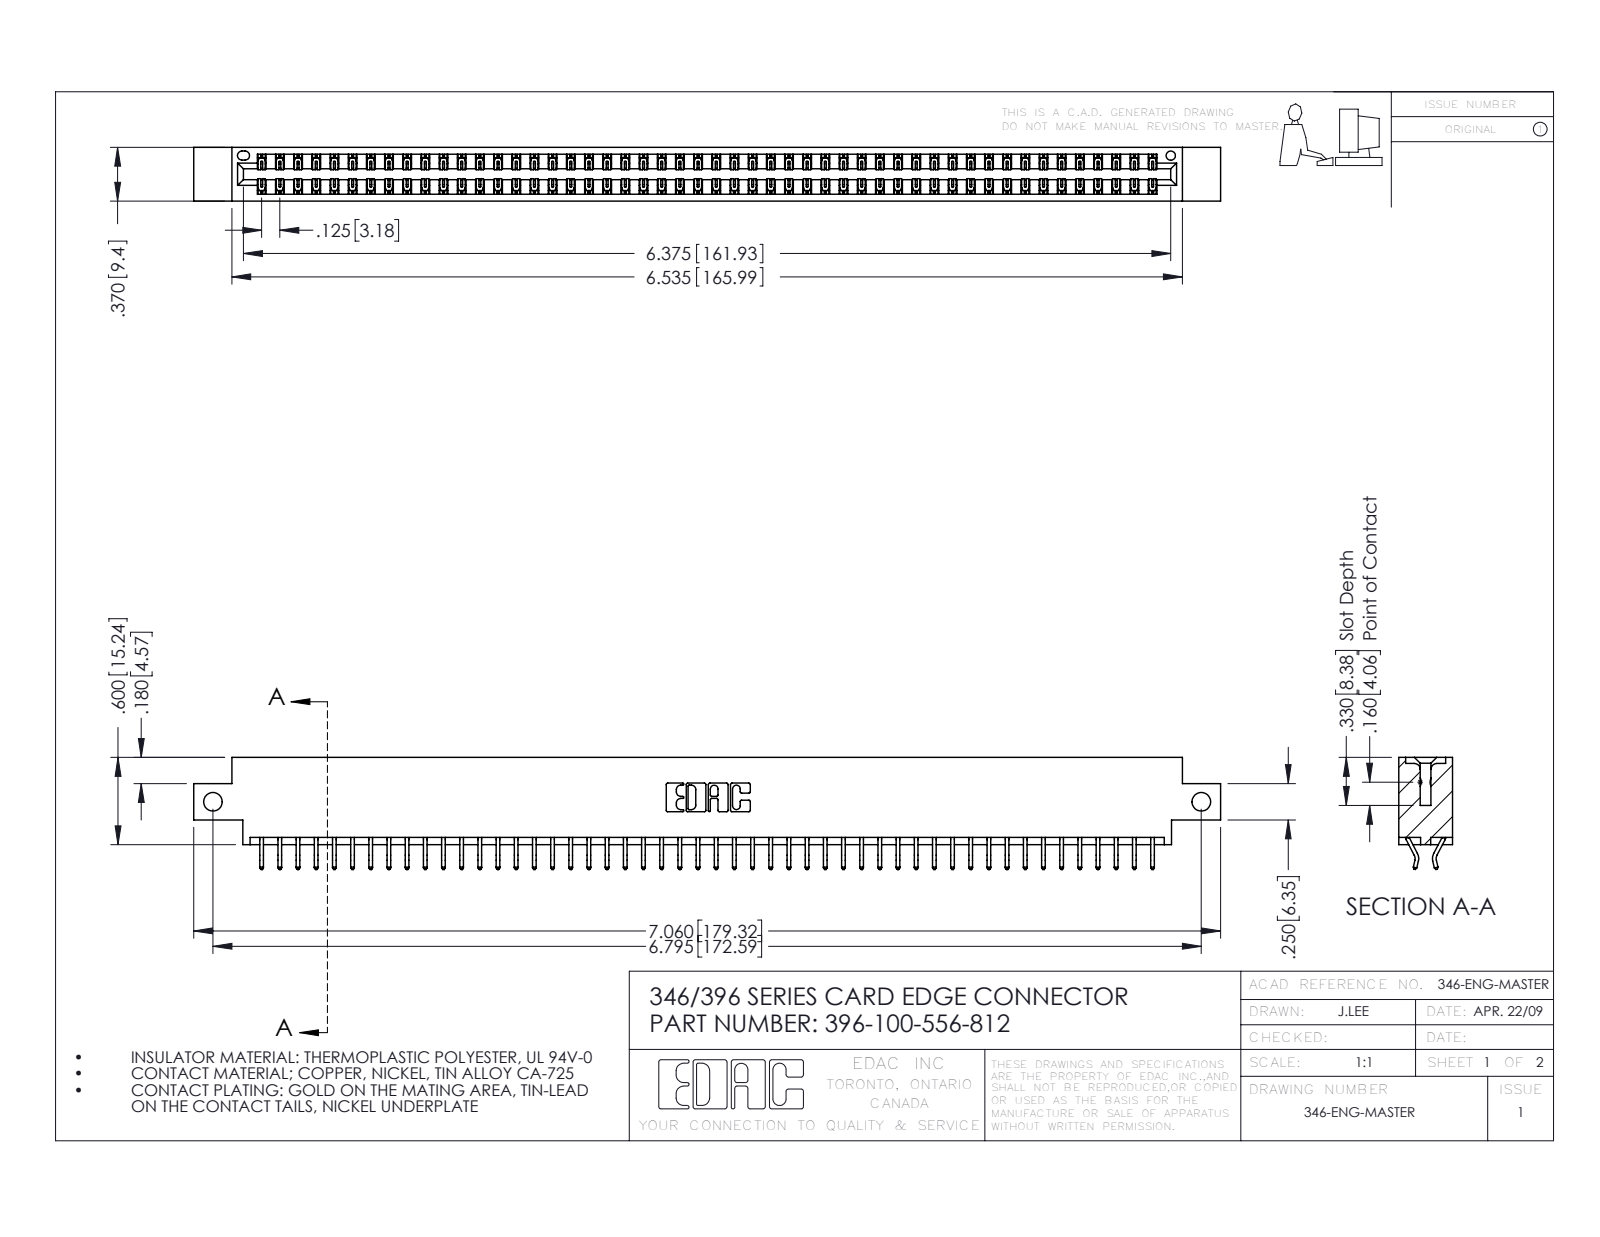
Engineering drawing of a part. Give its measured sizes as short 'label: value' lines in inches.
name: 345-292-001_556 Tail; 346 Part_0.170 Offset - Side Mount; 396-100-556-812
written by: SolidWorks 2016 (CONFIG_CONTROL_DESIGN)
unit: in
bodies: 101 solids, 5926 faces (3980 planar, 1946 cylindrical, 0 other)
size: 7.06 × 0.77 × 0.37
volume: 1.056 in³; area: 36.98 in²
holes: 2× ⌀0.128, 1× ⌀0.064
rounds: 150× R0.006, 22× R0.01, 6× R0.007, 6× R0.031, 3× R0.026, 2× R0.01, 2× R0.014, 2× R0.022
face distances: 0.048, 0.322, 0.37, 0.25, 0.025, 0.072, 0.298, 0.275, 0.148, 0.222
hole spacings: 6.795
